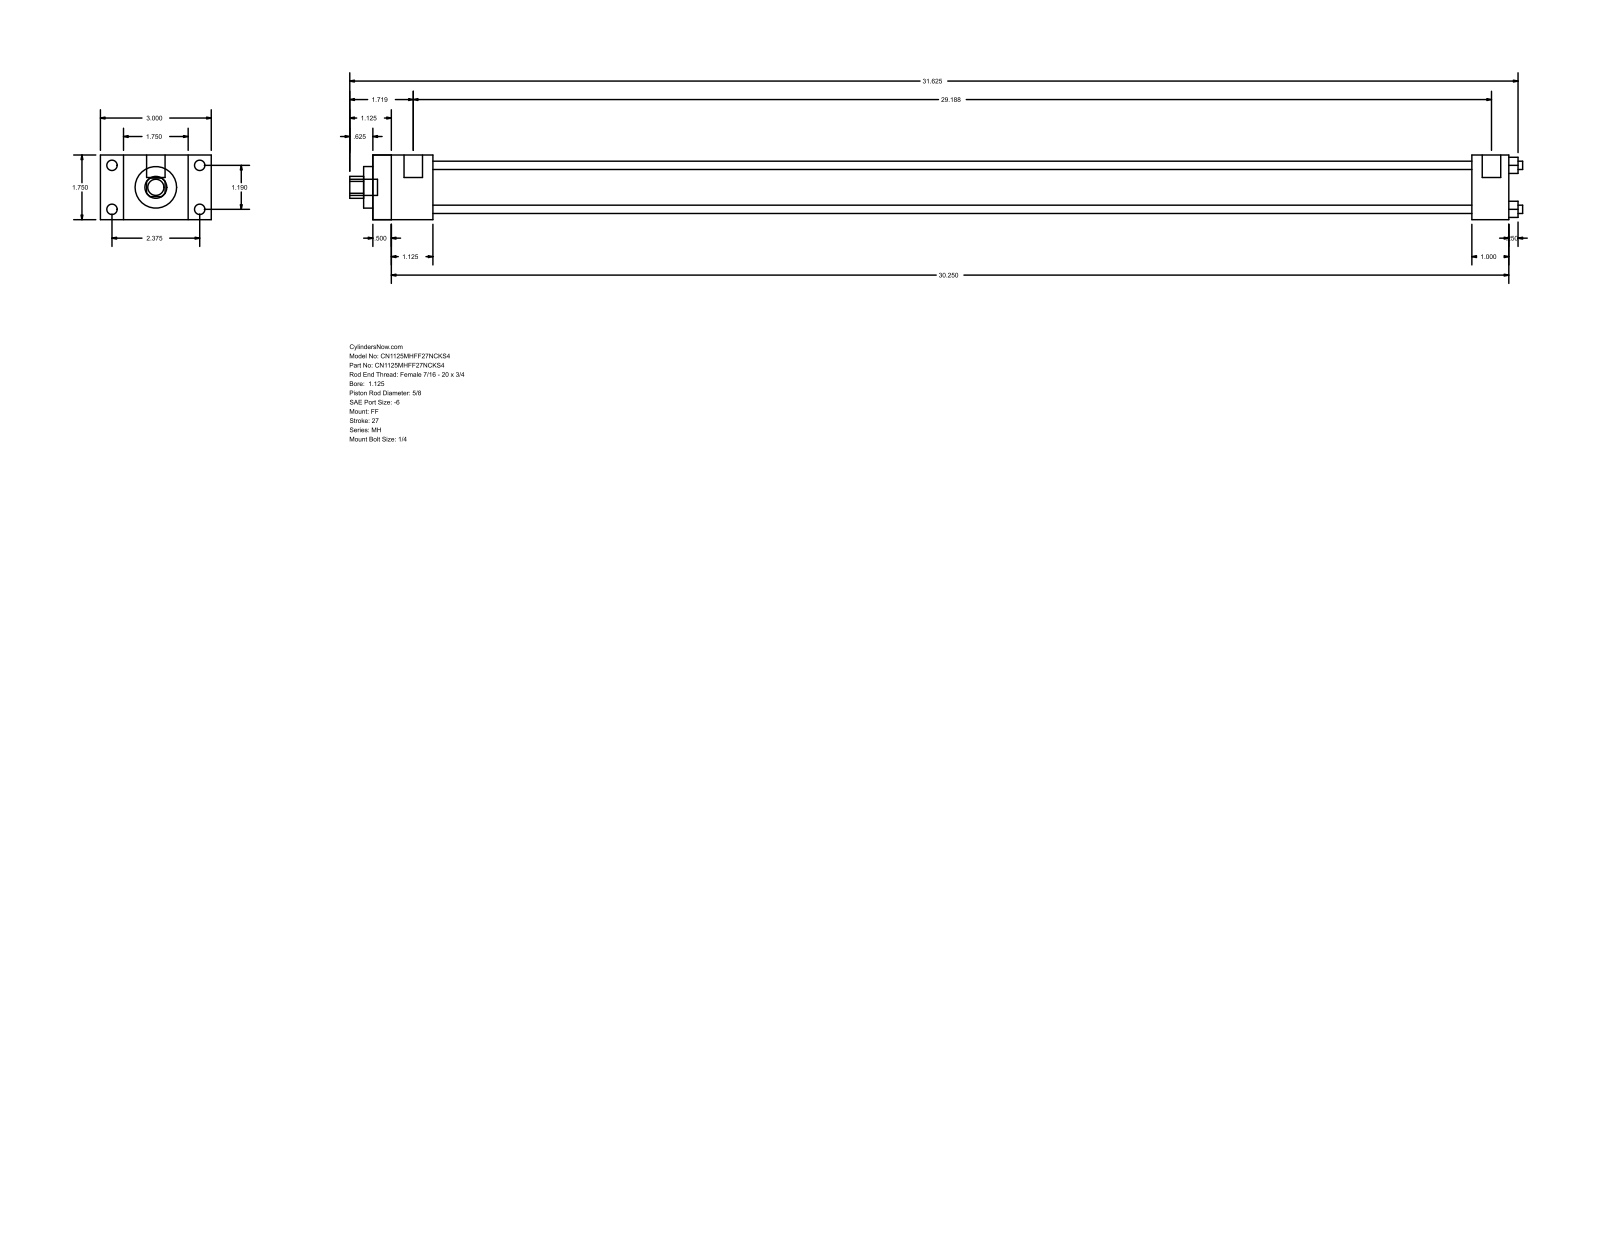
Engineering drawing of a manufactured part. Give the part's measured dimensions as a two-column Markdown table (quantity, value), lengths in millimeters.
| quantity | value |
| --- | --- |
| part name | MH_FF__0112_0.625 |
| STEP written by | GSSL Pune (CONFIG_CONTROL_DESIGN) |
| units | millimeters |
| bodies | 0 solids, 92 faces (64 planar, 28 cylindrical, 0 other) |
| overall size | 806.45 × 76.2 × 44.45 |
| round holes (diameter × count) | 5.71 × 4, 15.88 × 1, 28.57 × 1, 34.92 × 1 |
| round bosses / shafts (diameter × count) | 7.14 × 4, 5.56 × 4, 12.7 × 2, 11.11 × 1 |
| partial cylindrical surfaces (radius × count) | 7.54 × 1 |
| main face-to-face distances | 44.46, 781.04, 15.87, 12.69, 768.35, 60.33, 28.58, 41.27, 755.64, 742.95 |
| hole center spacings | 21.37, 30.22, 42.74 |
